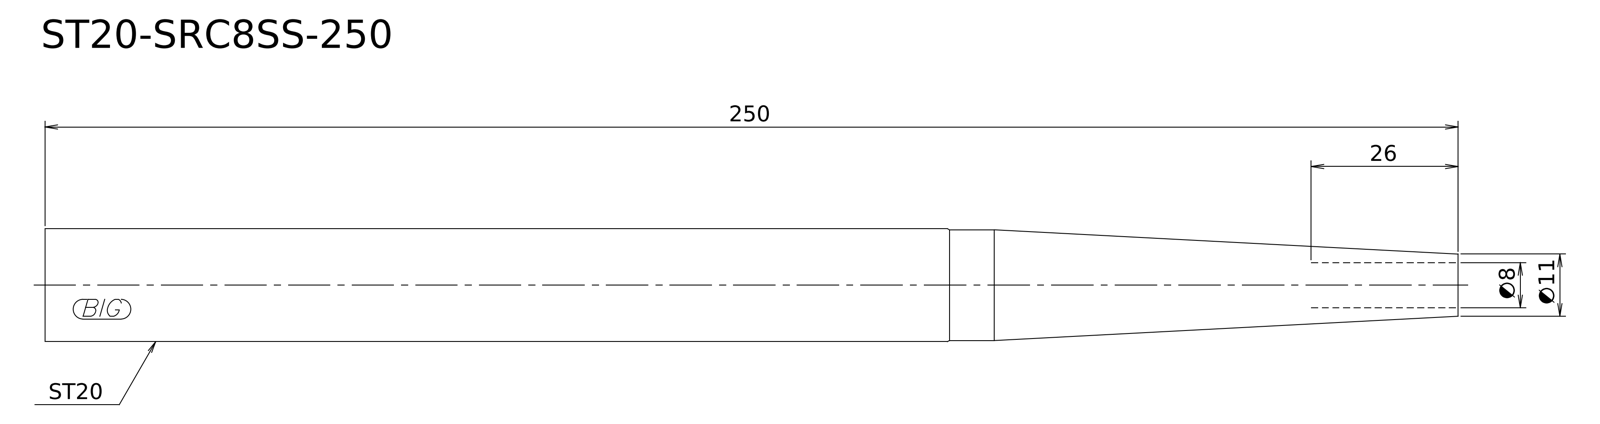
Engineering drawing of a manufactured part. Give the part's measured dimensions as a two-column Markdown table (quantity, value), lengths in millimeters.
| quantity | value |
| --- | --- |
| STEP written by | Kubotek KeyCreator V8.5.1 (14335) (CONFIG_CONTROL_DESIGN) |
| units | millimeters |
| bodies | 1 solid, 6 faces (2 planar, 2 cylindrical, 2 other) |
| overall size | 250 × 20 × 20 |
| volume | 68 144 mm³ |
| surface area | 14 904 mm² |
| round bosses / shafts (diameter × count) | 20 × 1, 19.6 × 1 |
| main face-to-face distances | 250 |
